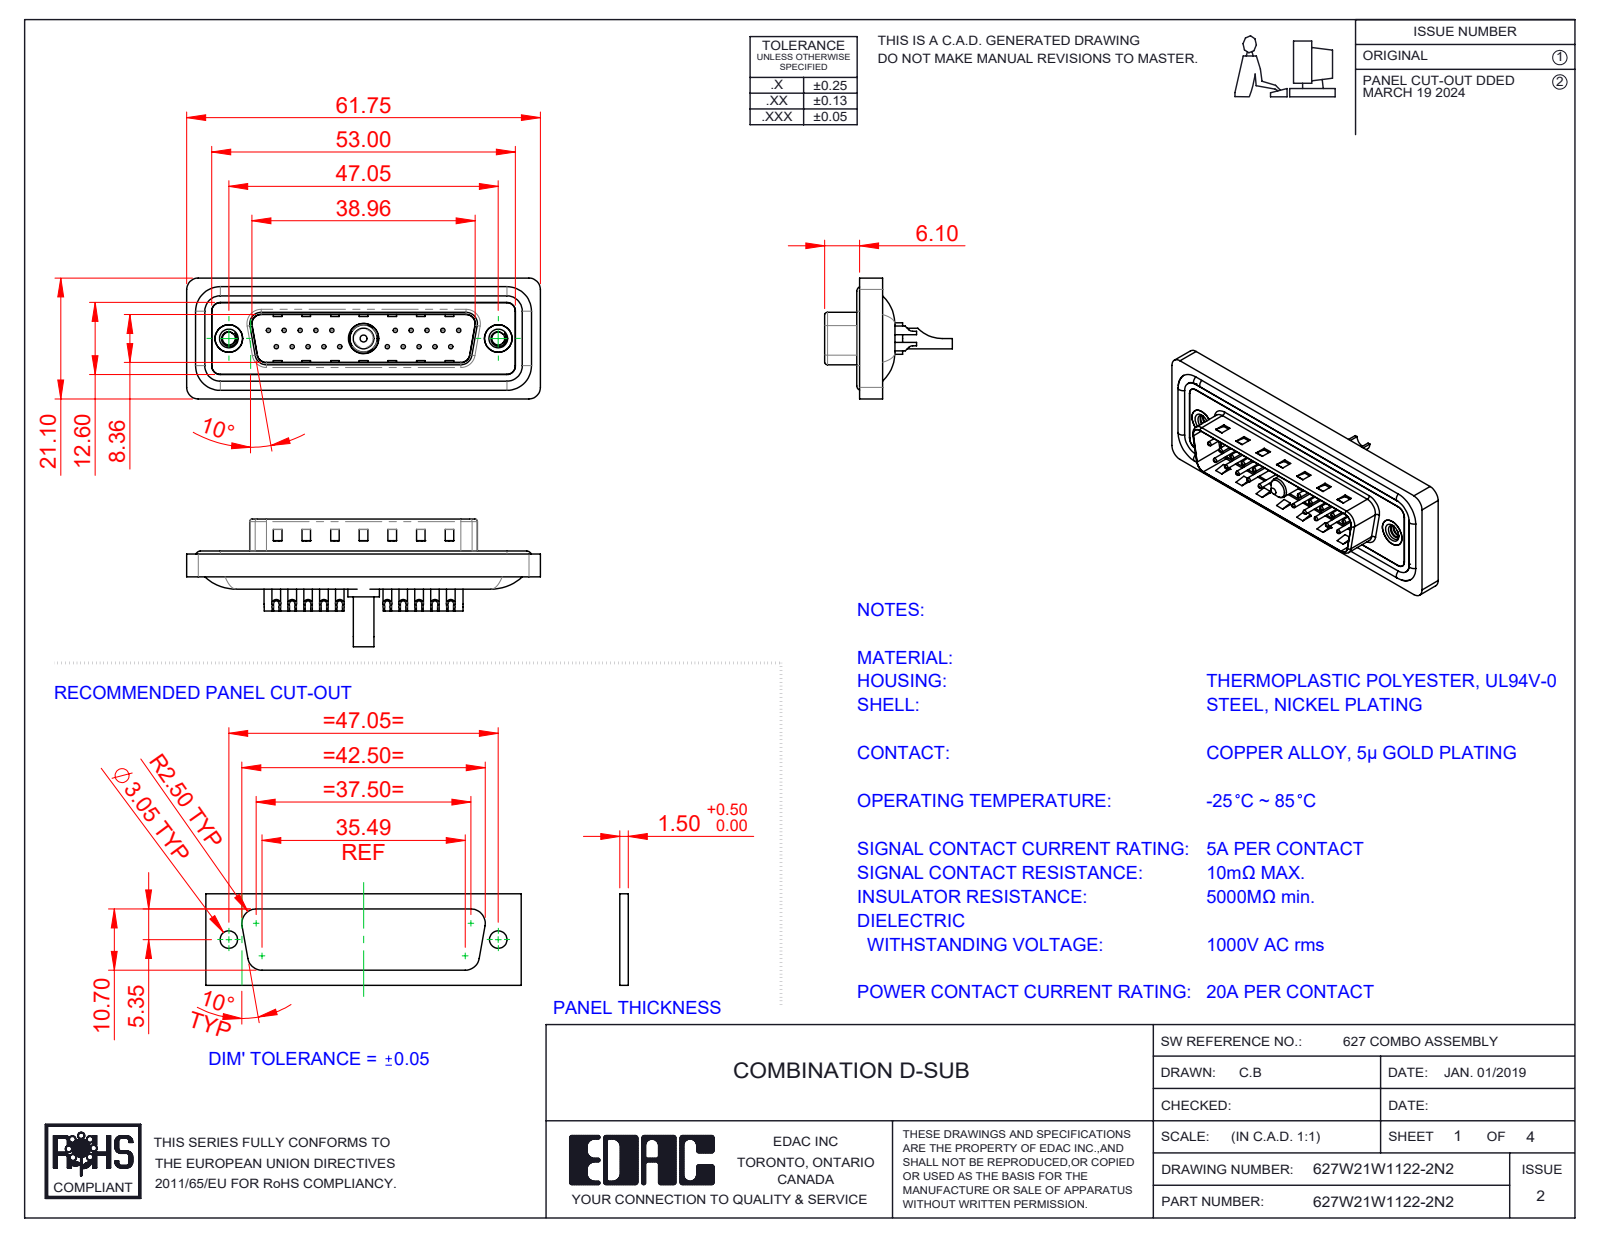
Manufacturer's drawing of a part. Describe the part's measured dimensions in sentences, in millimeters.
The part is named "627Combo Waterproof Housing_25 Contacts; 627Combo Shell Front_25 Contacts; 627Combo Threaded Rivet_2; 627W21W1122-2N2 (+5 more)". Its 3-D file was written by "SolidWorks 2023 (CONFIG_CONTROL_DESIGN)". It is 29 solids with 1268 faces: 402 planar, 530 cylindrical and 336 other. Overall it measures 61.75 by 22.3 by 21.1 millimeters. Its volume is 7 241 cubic millimeters and its surface area 12 195 square millimeters. Round holes: 20 of diameter 0.75, 20 of diameter 1, 20 of diameter 1.6, 20 of diameter 2, 2 of diameter 2.26, 2 of diameter 4, 2 of diameter 4.8, 2 of diameter 5, 1 of diameter 2.7, 1 of diameter 4.85, 1 of diameter 5.3. Round bosses or shafts: 20 of diameter 1.5, 4 of diameter 1.6, 2 of diameter 4.9, 1 of diameter 5.5, 1 of diameter 5.2, 1 of diameter 4.75, 1 of diameter 3.75, 1 of diameter 3.6. Partial cylindrical surfaces (rounded edges, fillets, slot ends): 22 of radius 1.5, 18 of radius 2, 8 of radius 0.5, 8 of radius 1.6, 6 of radius 1, 4 of radius 0.25, 4 of radius 0.6, 4 of radius 0.65. The main face-to-face distances are 0.4, 1.5, 1.1, 1.6, 0.5, 3.1, 2.9, 4.1, 0.82, 9.58. The hole center spacings are 3.16, 2.77, 5.54, 8.31, 5.04, 19.39, 20.97, 22.16.
